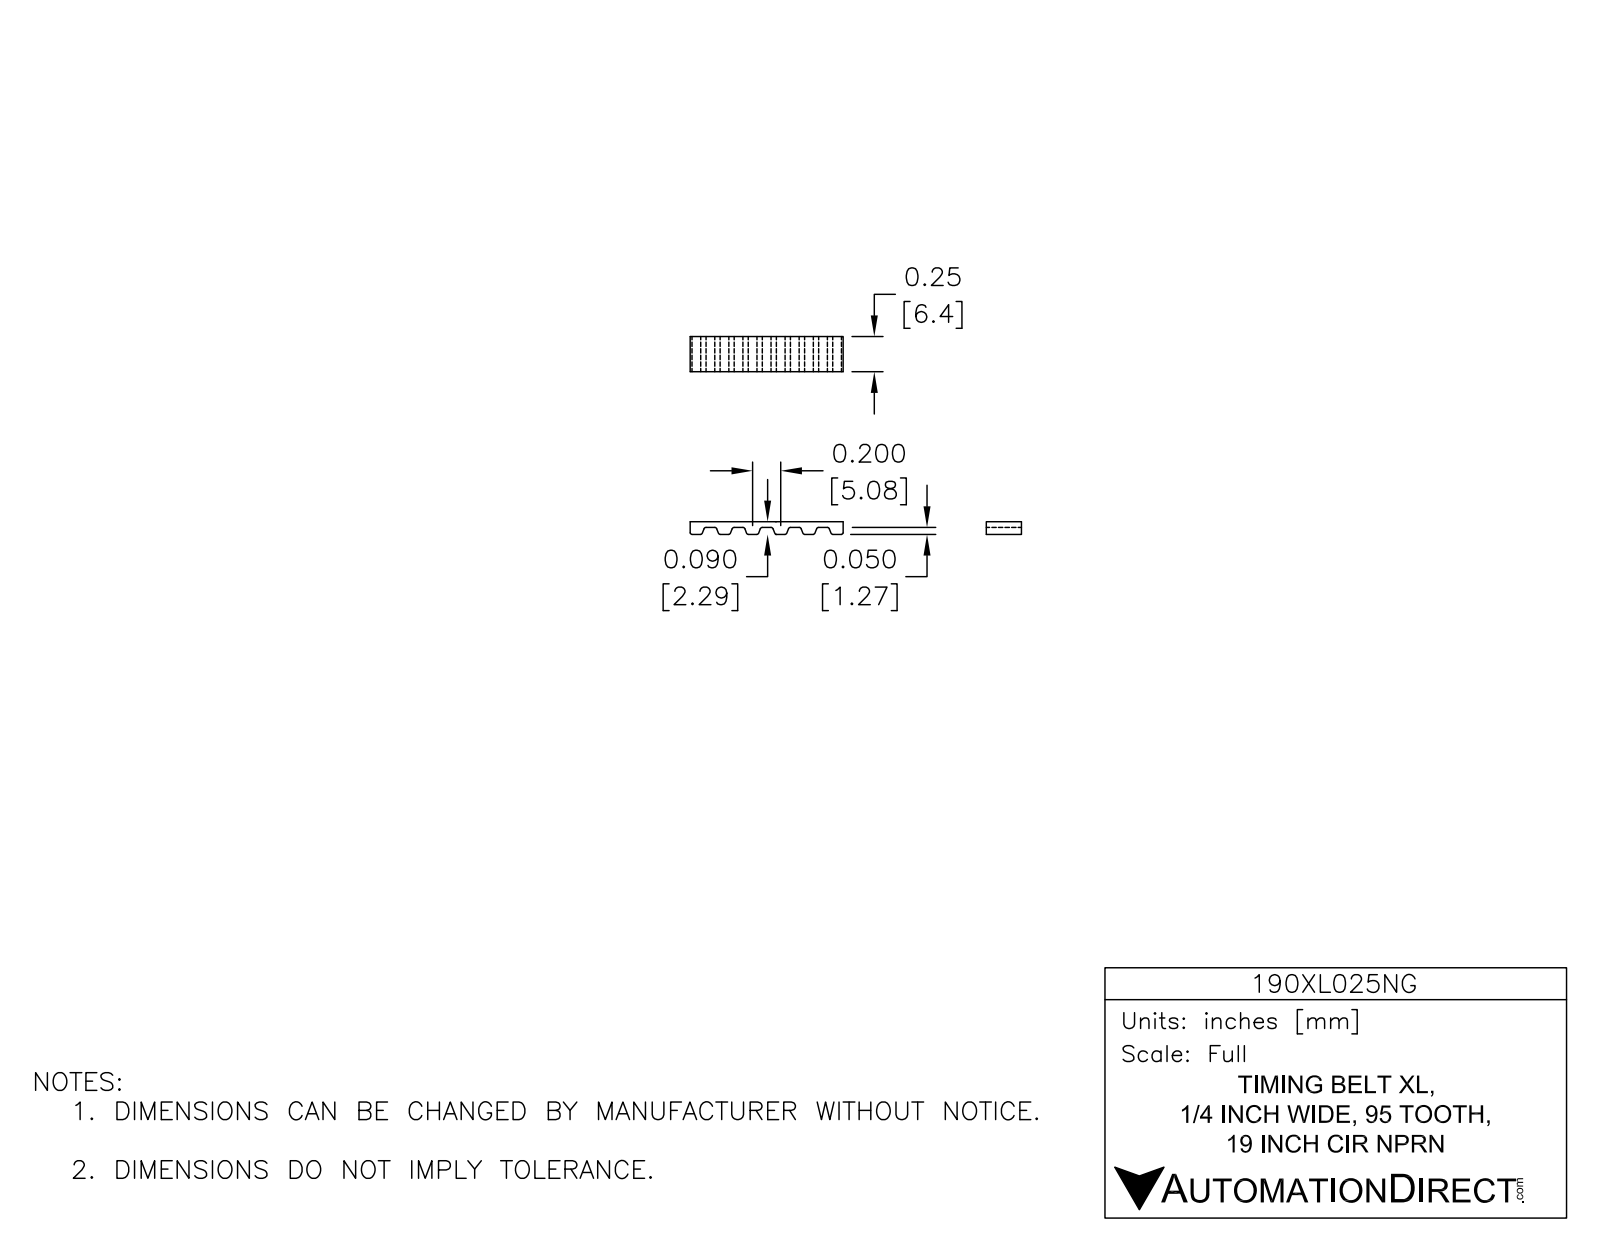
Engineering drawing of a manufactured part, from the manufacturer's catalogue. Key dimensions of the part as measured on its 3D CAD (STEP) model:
Part name (STEP PRODUCT): 190XL025NG
STEP written by: SolidWorks 2014 (AUTOMOTIVE_DESIGN)
Units: inches
Bodies: 1 solid, 800 faces (338 planar, 462 cylindrical, 0 other)
Overall size (bounding box): 7.788 × 3 × 0.25
Volume: 0.258 in³ · Surface area: 12.81 in²
Partial cylindrical surfaces — rounded edges, fillets, slot ends (radius × count): R0.015 ×380, R1.46 ×2, R1.5 ×2
Main face-to-face distances: 3, 0.04, 2.96, 0.25, 2.92, 0.179, 1.073, 0.09, 2.91, 0.05
